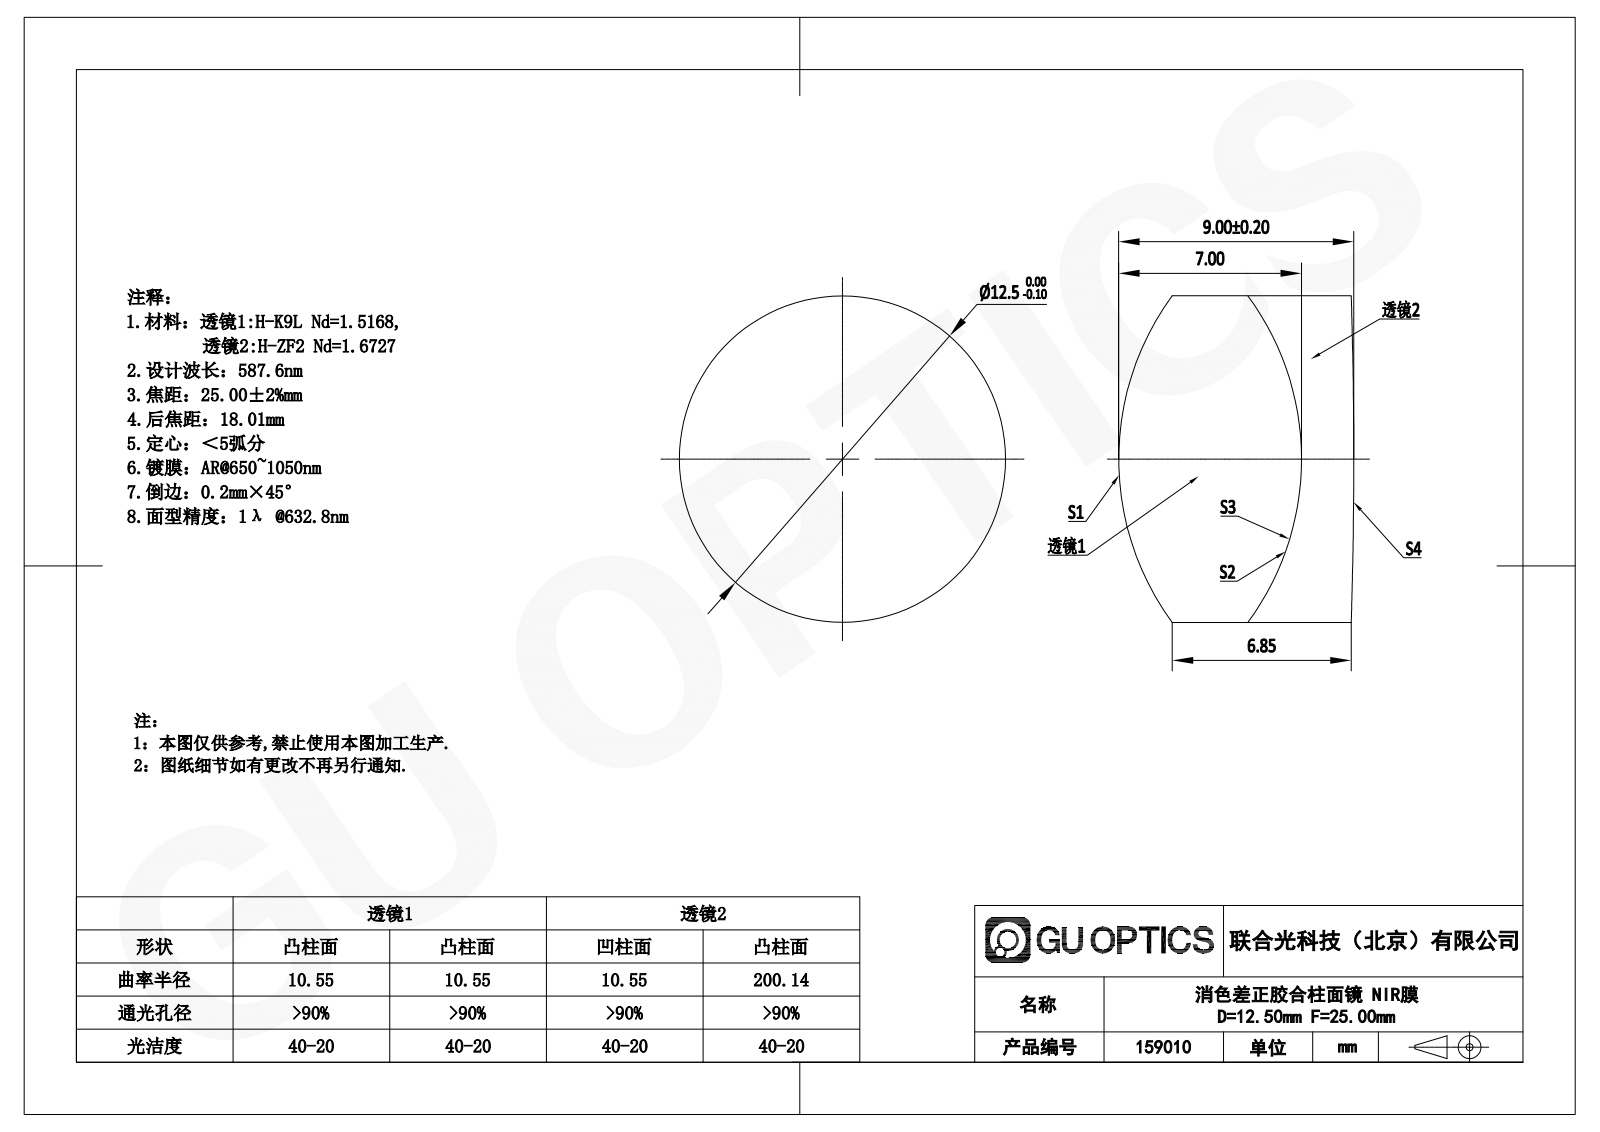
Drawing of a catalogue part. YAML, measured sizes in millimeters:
part_name: "159010"
step_written_by: "SolidWorks 2020 (CONFIG_CONTROL_DESIGN)"
units: millimeters
bodies: {solids: 1, faces: 5, planar: 0, cylindrical: 5, other: 0}
overall_size: [12.5, 12.5, 9]
volume: 1042
surface_area: 564
round_bosses_or_shafts:
  - {diameter: 12.5, count: 1}
partial_cylinders:
  - {radius: 10.55, count: 1}
  - {radius: 200.14, count: 1}
